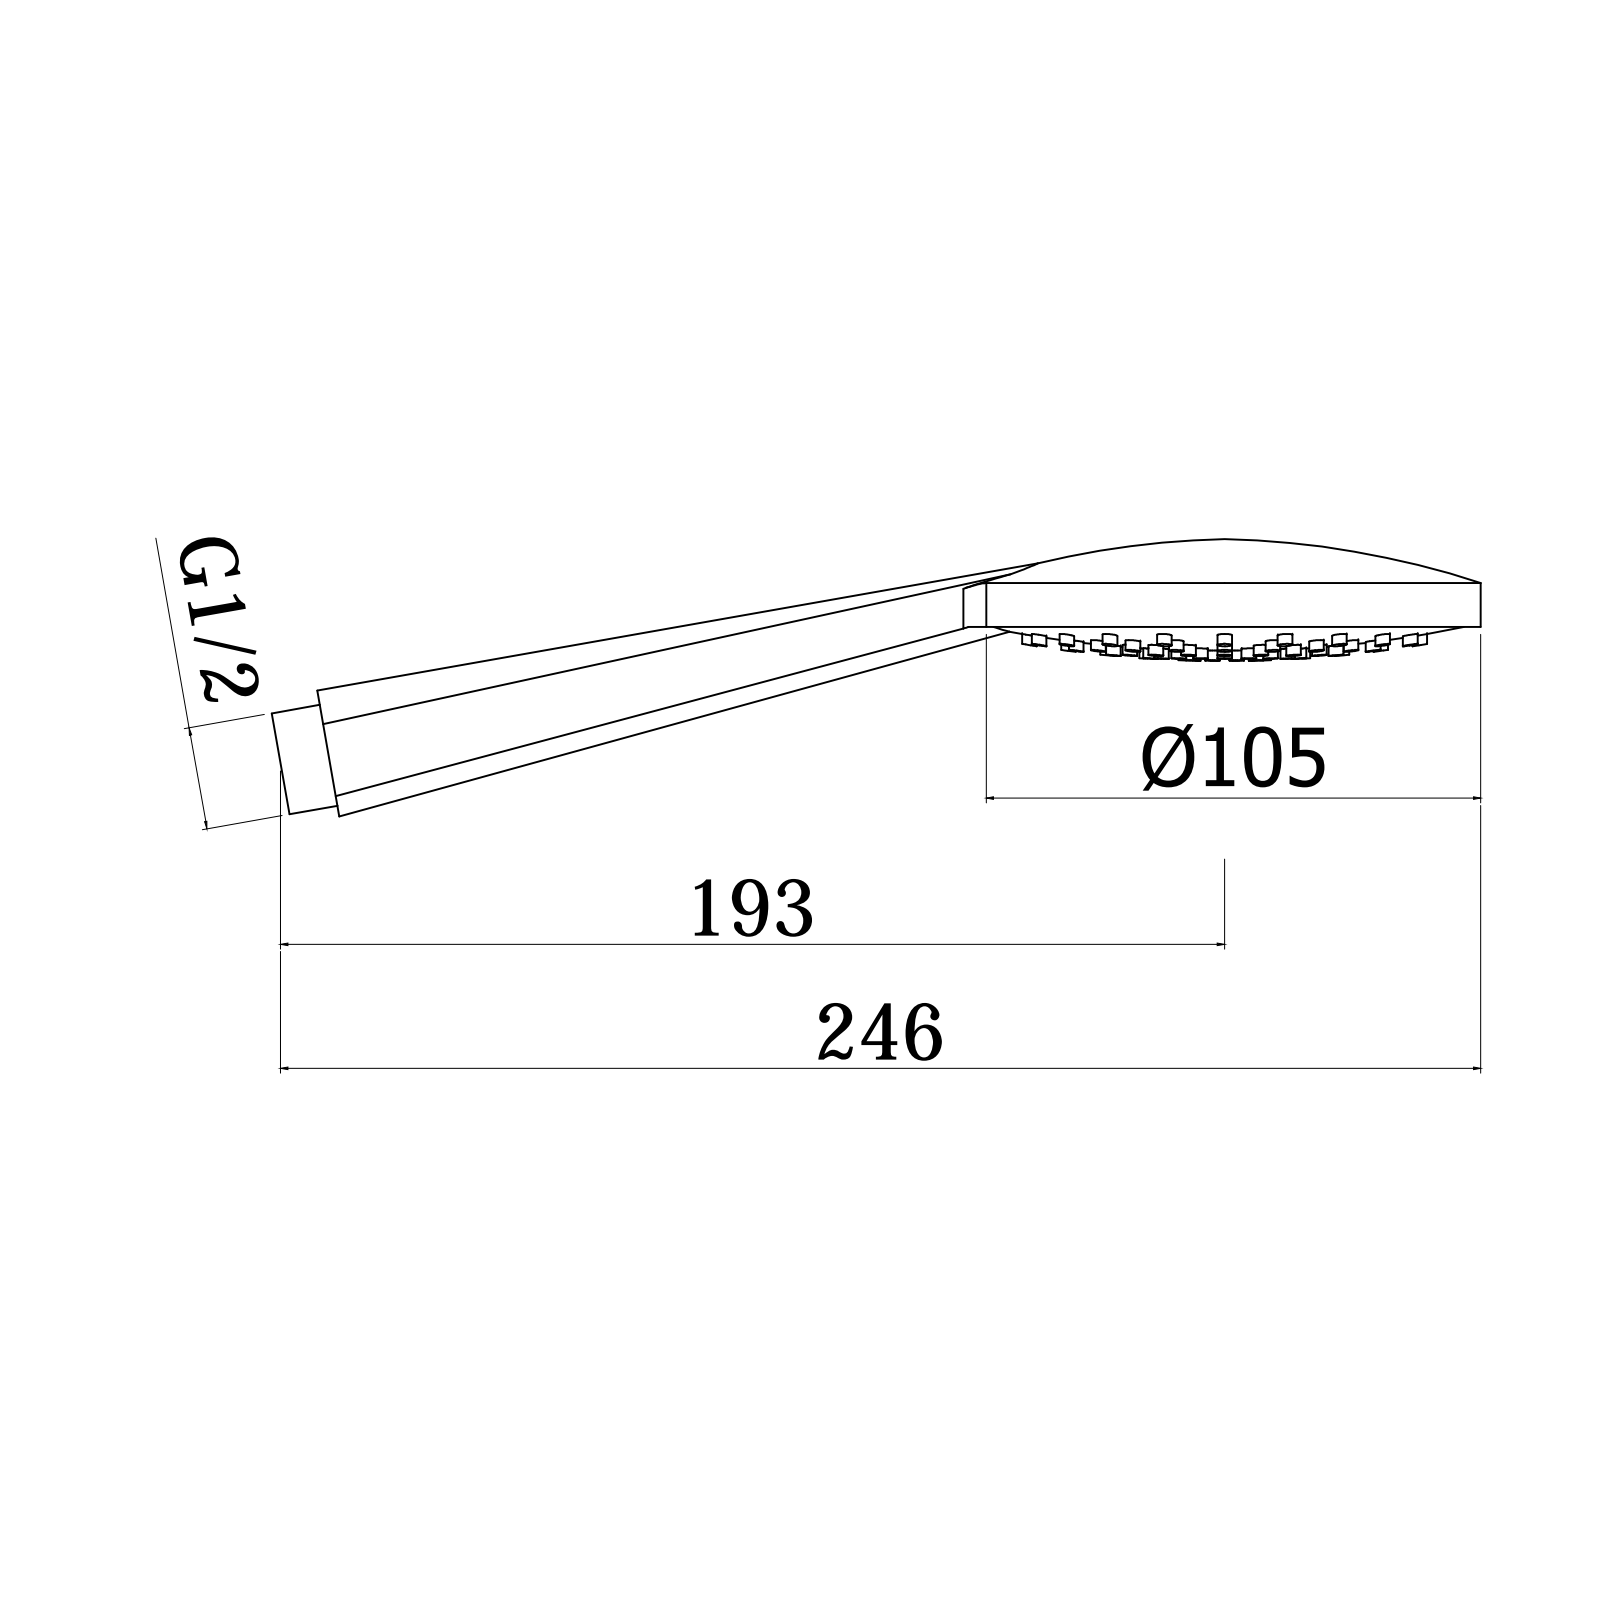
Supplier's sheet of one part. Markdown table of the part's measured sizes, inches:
| quantity | value |
| --- | --- |
| part name | ZDOC105CR |
| STEP written by | CREO PARAMETRIC BY PTC INC, 2020044 (CONFIG_CONTROL_DESIGN) |
| units | inches |
| bodies | 1 solid, 2505 faces (1072 planar, 173 cylindrical, 1260 other) |
| overall size | 9.563 × 4.132 × 2.111 |
| volume | 5.663 in³ |
| surface area | 138.2 in² |
| round holes (diameter × count) | 0.276 × 2, 0.134 × 1, 0.177 × 1, 0.236 × 1, 0.386 × 1, 0.425 × 1, 0.433 × 1, 0.457 × 1, 0.551 × 1, 0.583 × 1, 0.591 × 1, 3.445 × 1 |
| round bosses / shafts (diameter × count) | 3.886 × 1, 3.547 × 1, 0.819 × 1, 0.728 × 1, 0.724 × 1, 0.709 × 1, 0.572 × 1, 0.551 × 1 |
| partial cylindrical surfaces (radius × count) | 0.02 × 13, 0.012 × 10, 0.009 × 8, 0.106 × 8, 0.394 × 8, 0.039 × 6, 0.091 × 4, 0.118 × 4 |
| main face-to-face distances | 0.346, 0.189, 0.228, 0.091, 0.137, 0.098, 0.118, 0.571, 0.039, 0.157 |
| hole center spacings | 0.627, 1.354, 1.201, 1.254 |
